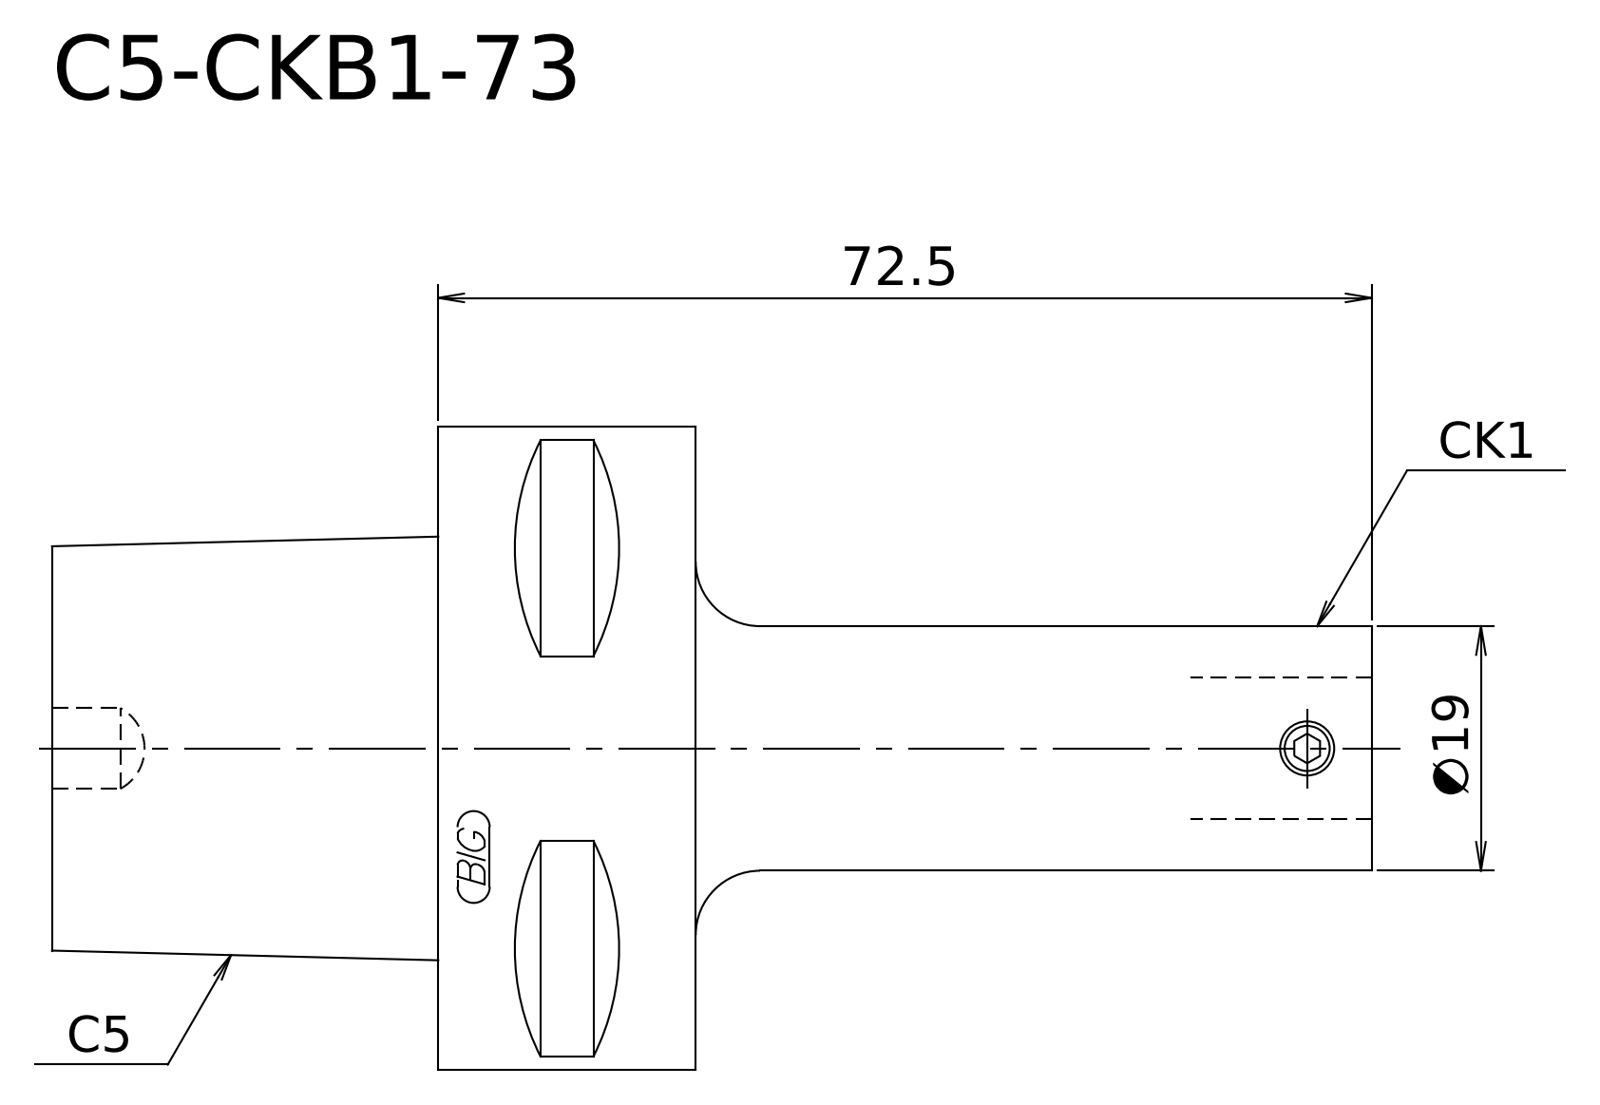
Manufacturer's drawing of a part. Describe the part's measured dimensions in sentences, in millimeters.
Its 3-D file was written by "Kubotek KeyCreator V8.5.1 (14335) (CONFIG_CONTROL_DESIGN)". It is 1 solid with 8 faces: 4 planar, 2 cylindrical and 2 other. Overall it measures 102.5 by 49.98 by 49.98 millimeters. Its volume is 82 227 cubic millimeters and its surface area 13 217 square millimeters. Round bosses or shafts: 1 of diameter 49.98, 1 of diameter 19. The main face-to-face distances are 20, 50, 30, 52.5, 72.5, 102.5.
